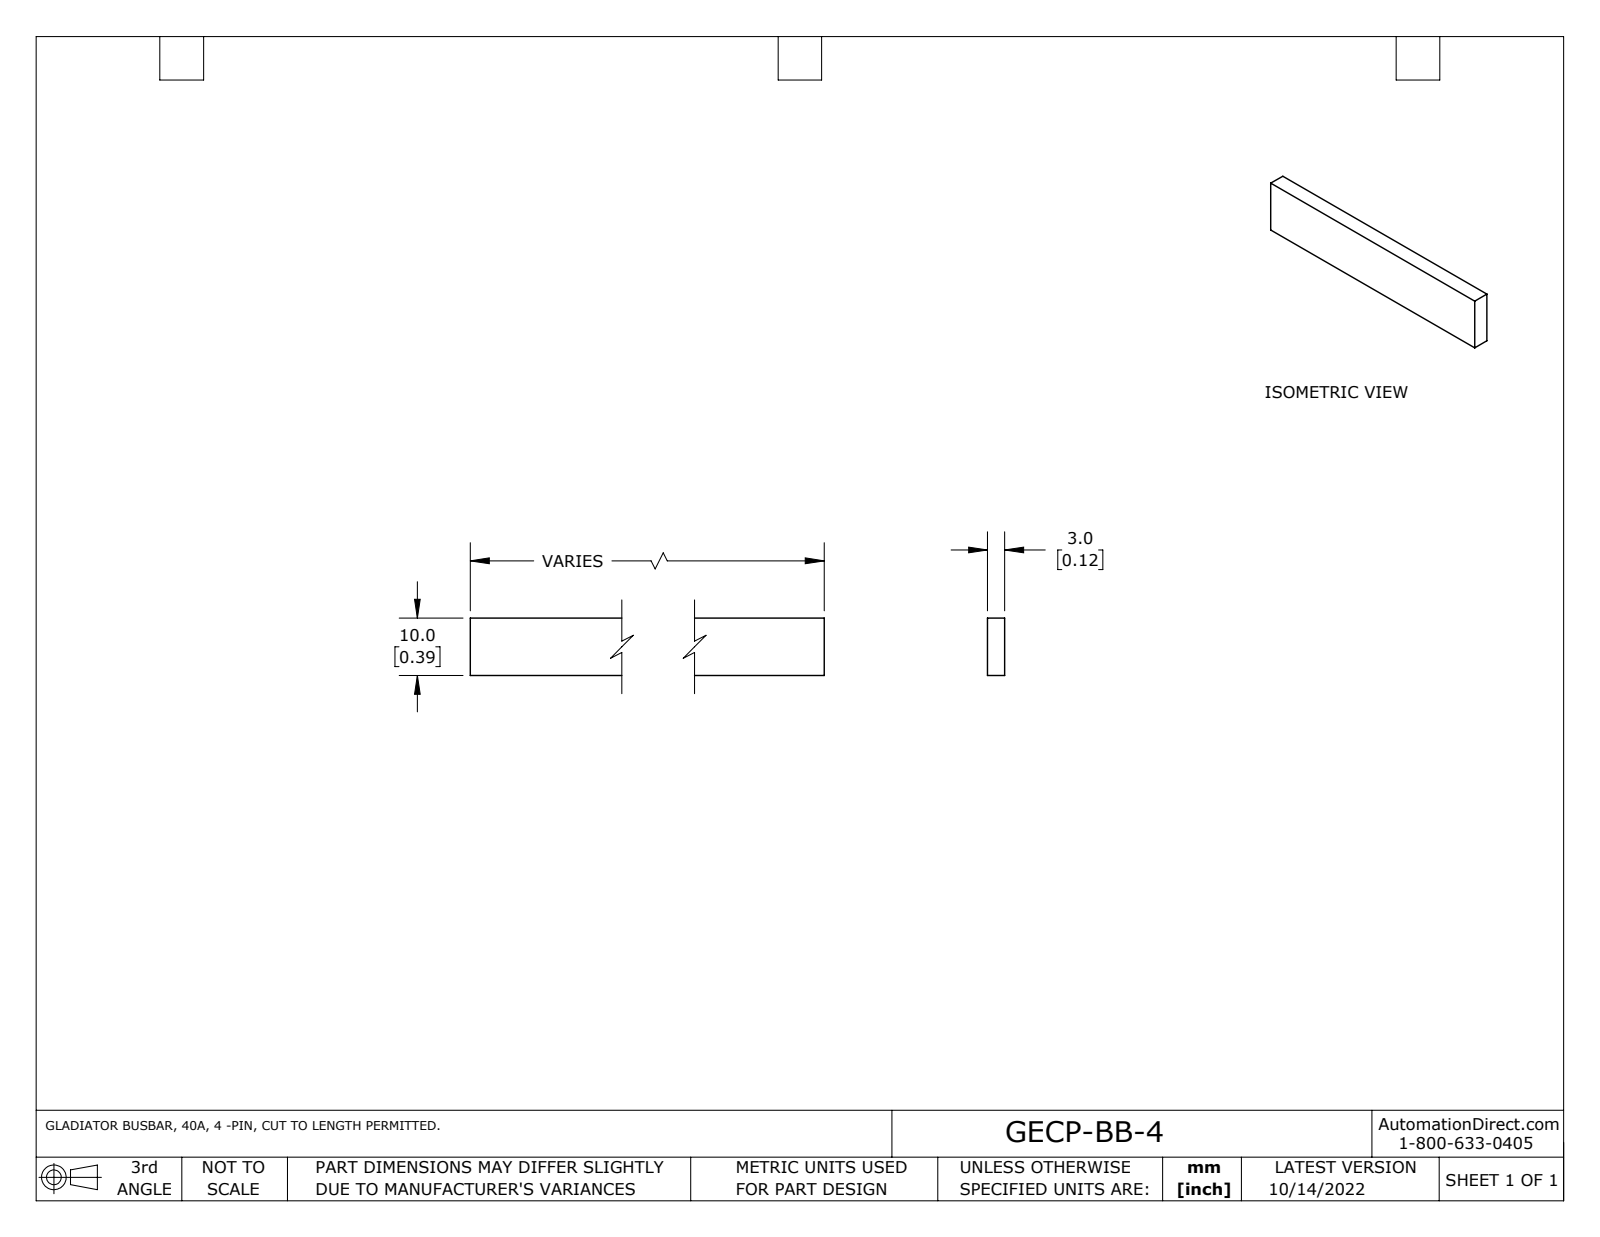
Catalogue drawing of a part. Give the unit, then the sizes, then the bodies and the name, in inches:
Units: inches
Overall size (bounding box): 1.984 × 0.394 × 0.118
Main face-to-face distances: 0.118, 0.394, 1.984
Volume: 0.092 in³ · Surface area: 2.124 in²
Bodies: 1 solid, 6 faces (6 planar, 0 cylindrical, 0 other)
Part name (STEP PRODUCT): GECP-BB-4
STEP written by: SolidWorks 2021 (AUTOMOTIVE_DESIGN)
